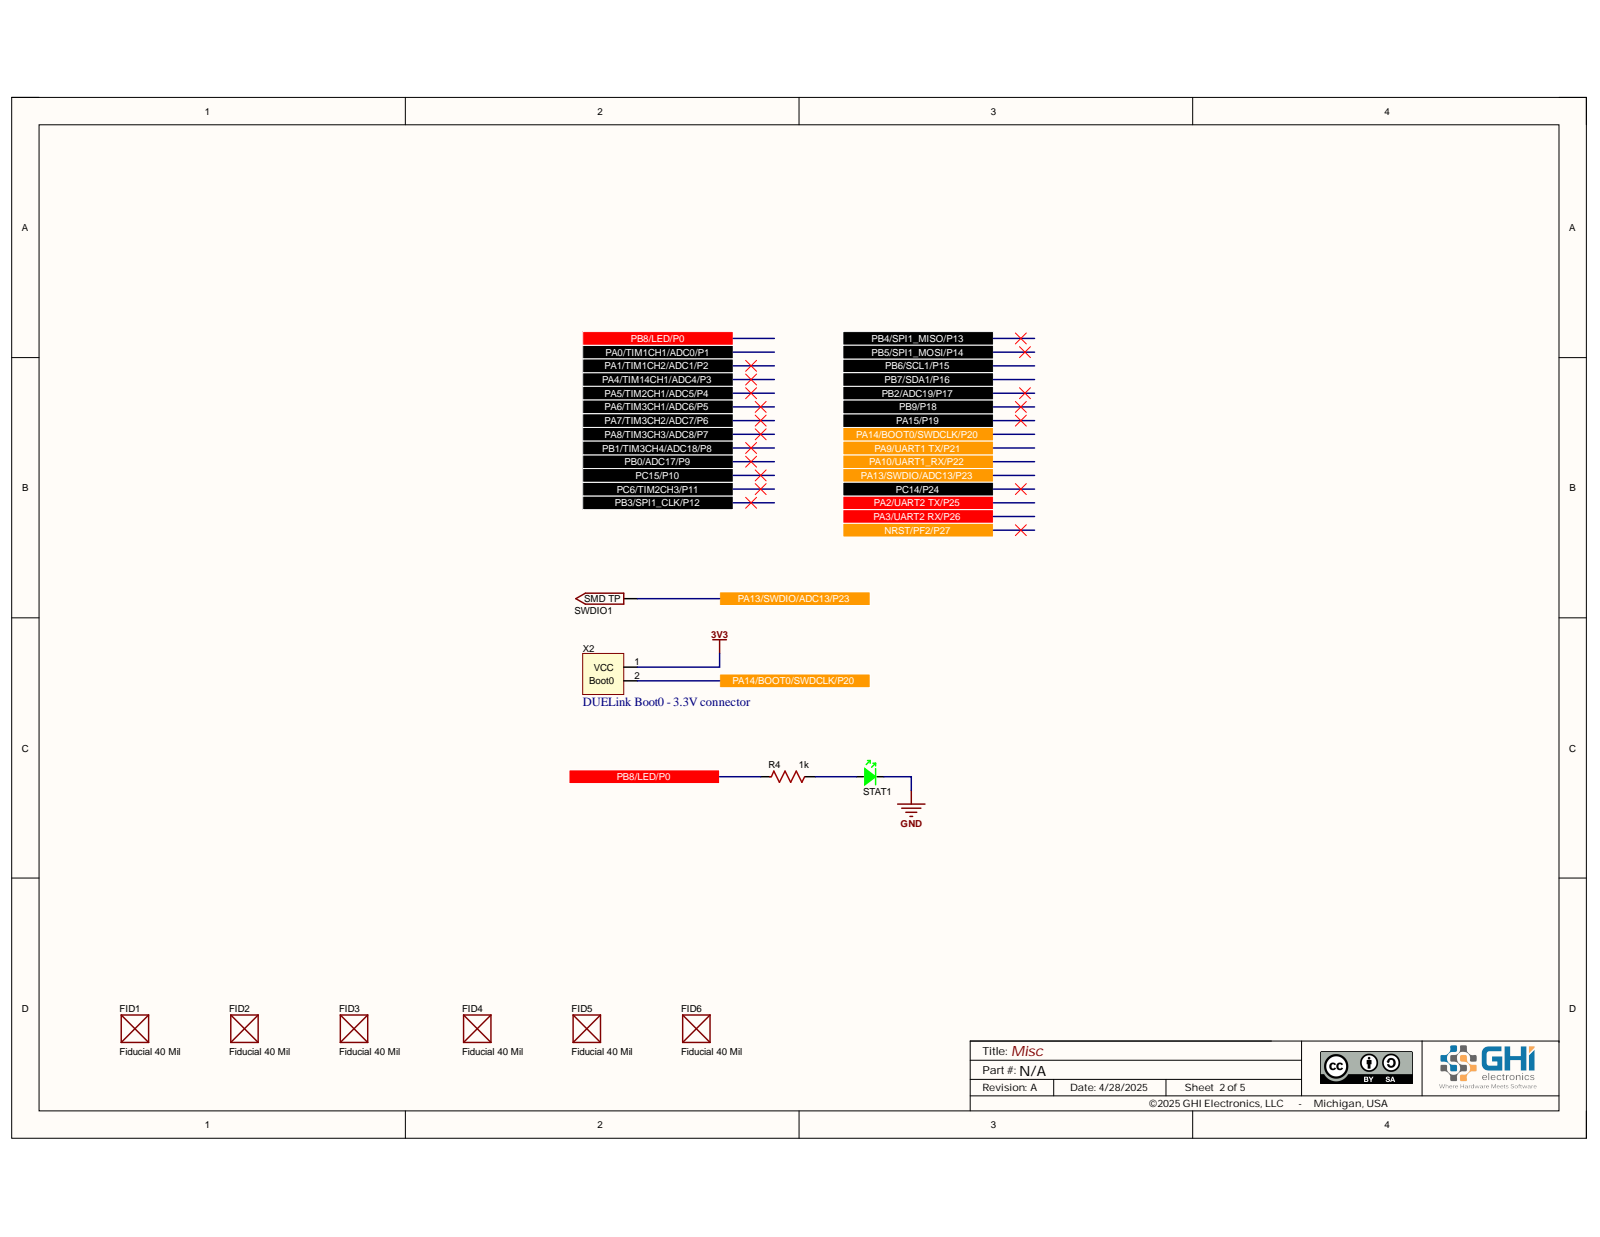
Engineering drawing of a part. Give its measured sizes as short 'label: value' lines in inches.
name: PCB; Board; R2; User Library-R SMD 0402 (+7 more)
written by: Open CASCADE 7.5 (AUTOMOTIVE_DESIGN)
unit: in
bodies: 453 solids, 8467 faces (5157 planar, 237 cylindrical, 3073 other)
size: 2.244 × 1.26 × 0.69
volume: 0.355 in³; area: 16.78 in²
holes: 5× ⌀0.039, 4× ⌀0.118, 2× ⌀0.04
rounds: 35× R0.005, 26× R0.006, 4× R0.138, 2× R0.007, 2× R0.007, 2× R0.007
face distances: 0.063, 0.275, 0.212, 0.338, 0.063, 1.26, 0.266, 0.072, 0.339, 0.276
hole spacings: 0.1, 0.2, 0.3, 0.984, 1.18, 1.268, 1.358, 1.449
